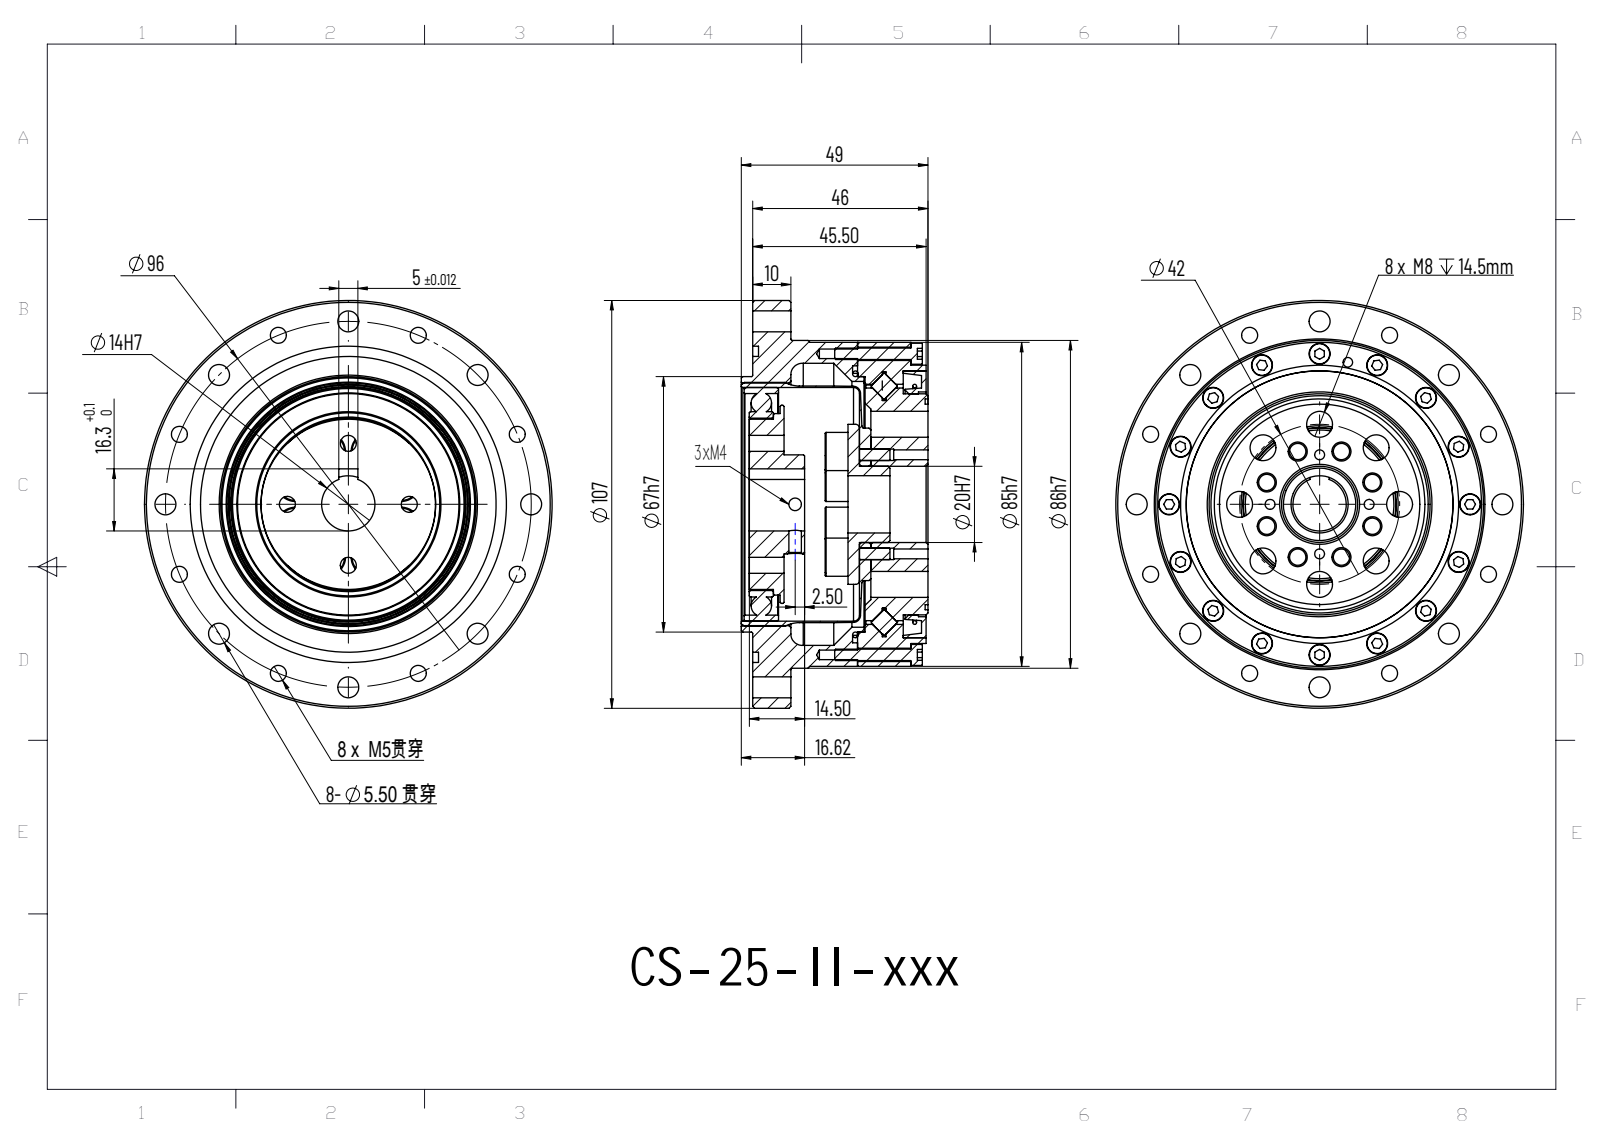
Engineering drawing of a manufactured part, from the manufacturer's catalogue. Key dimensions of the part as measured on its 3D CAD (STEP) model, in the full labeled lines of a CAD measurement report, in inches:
Part name (STEP PRODUCT): CS-25-II; ???????; ??; 25-160?? (+8 more)
STEP written by: ONSHAPE BY PTC INC, 1.201 (AP242_MANAGED_MODEL_BASED_3D_ENGINEERING_MIM_LF)
Units: inches
Bodies: 86 solids, 969 faces (407 planar, 253 cylindrical, 309 other)
Overall size (bounding box): 4.213 × 4.213 × 1.929
Volume: 11.94 in³ · Surface area: 187.9 in²
Round holes (diameter × count): ⌀0.098 ×17, ⌀0.138 ×16, ⌀0.165 ×12, ⌀0.197 ×8, ⌀0.217 ×8, ⌀0.26 ×8, ⌀0.268 ×8, ⌀0.102 ×4, ⌀0.118 ×4, ⌀0.13 ×2, ⌀0.126 ×1, ⌀0.228 ×1
Round bosses / shafts (diameter × count): ⌀0.157 ×48, ⌀0.217 ×16, ⌀0.118 ×16, ⌀0.394 ×8, ⌀0.236 ×8, ⌀4.213 ×1, ⌀3.386 ×1, ⌀3.346 ×1
Main face-to-face distances: 0.709, 0.689, 0.02, 0.394, 1.083, 1.102, 0.827, 0.118, 0.236, 0.591
Hole centre spacings: 0.737, 1.363, 1.446, 1.53, 1.751, 1.89, 1.98, 2.1
